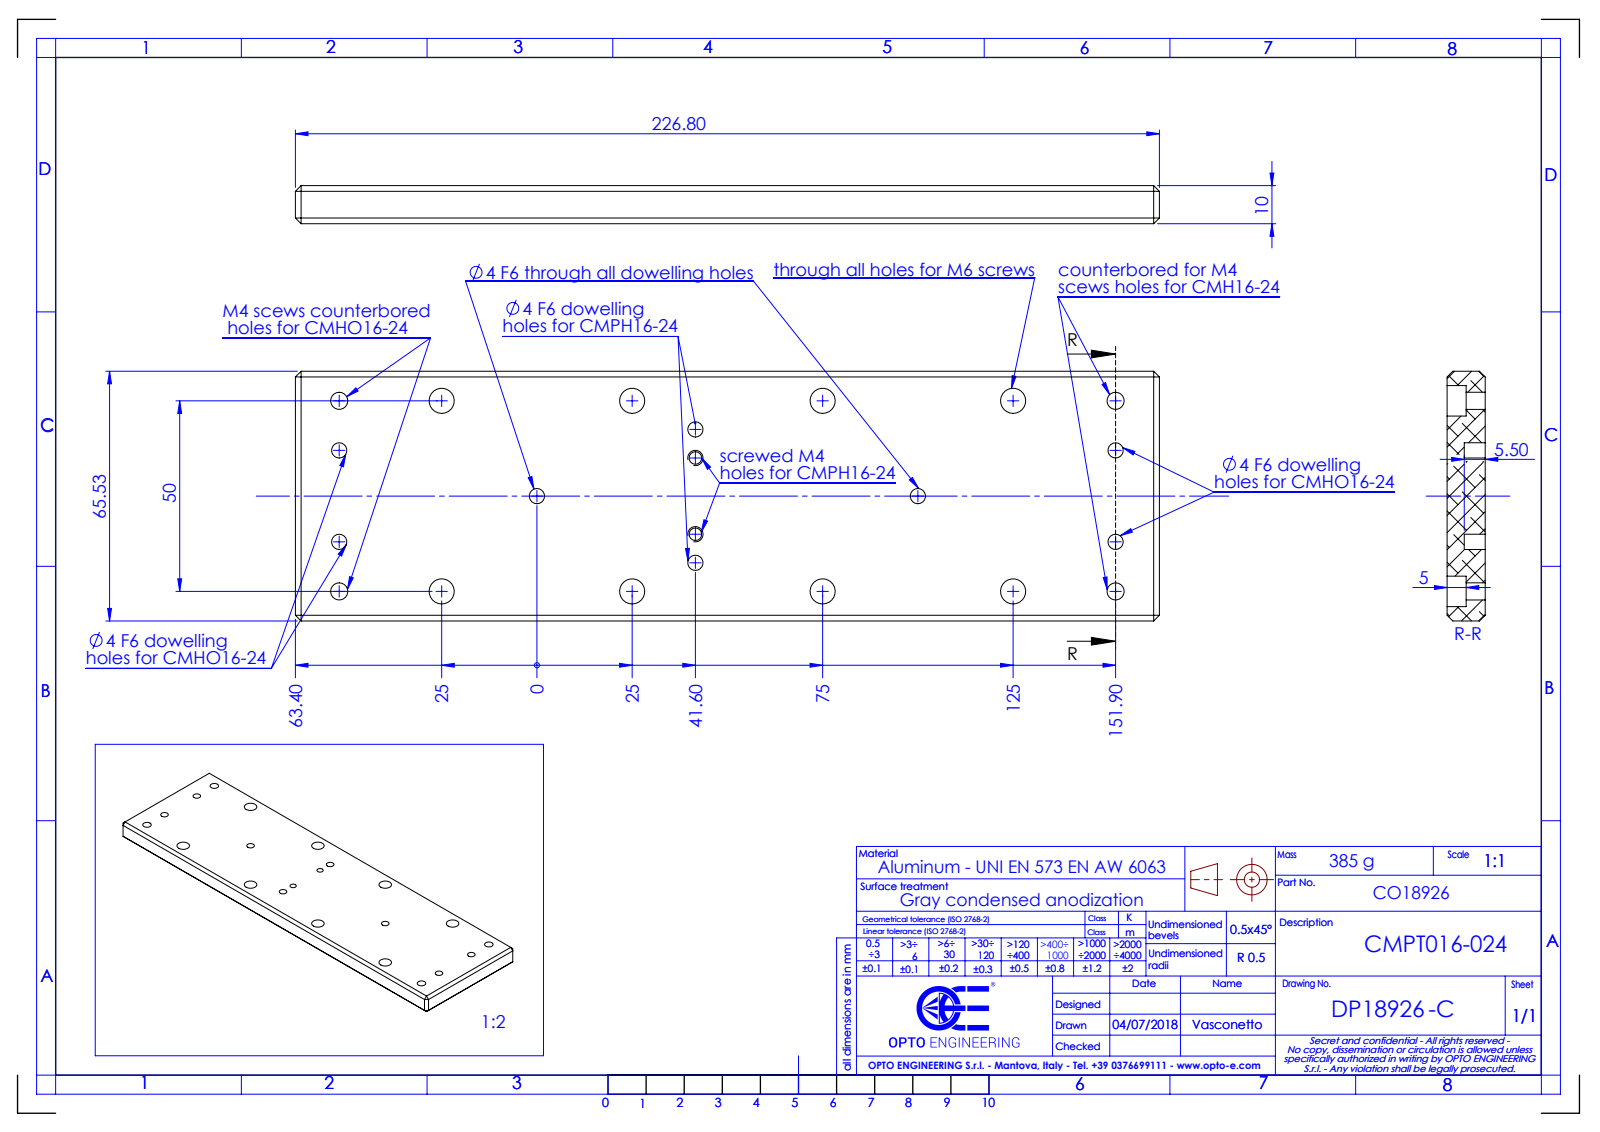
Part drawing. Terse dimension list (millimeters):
name: CMPT16-24
written by: SolidWorks 2021 (AUTOMOTIVE_DESIGN)
unit: mm
bodies: 1 solid, 88 faces (36 planar, 52 cylindrical, 0 other)
size: 226.8 × 65.53 × 10
volume: 142 399 mm³; area: 37 033 mm²
holes: 8× ⌀4, 8× ⌀6.6, 4× ⌀4.5, 4× ⌀8, 2× ⌀3.3
face distances: 10, 65.52, 51.27, 226.8, 5, 165.3, 4.5, 5.5, 0.5, 204.55
hole spacings: 50, 35.36, 70.71, 100, 13, 26.9, 29.88, 37
